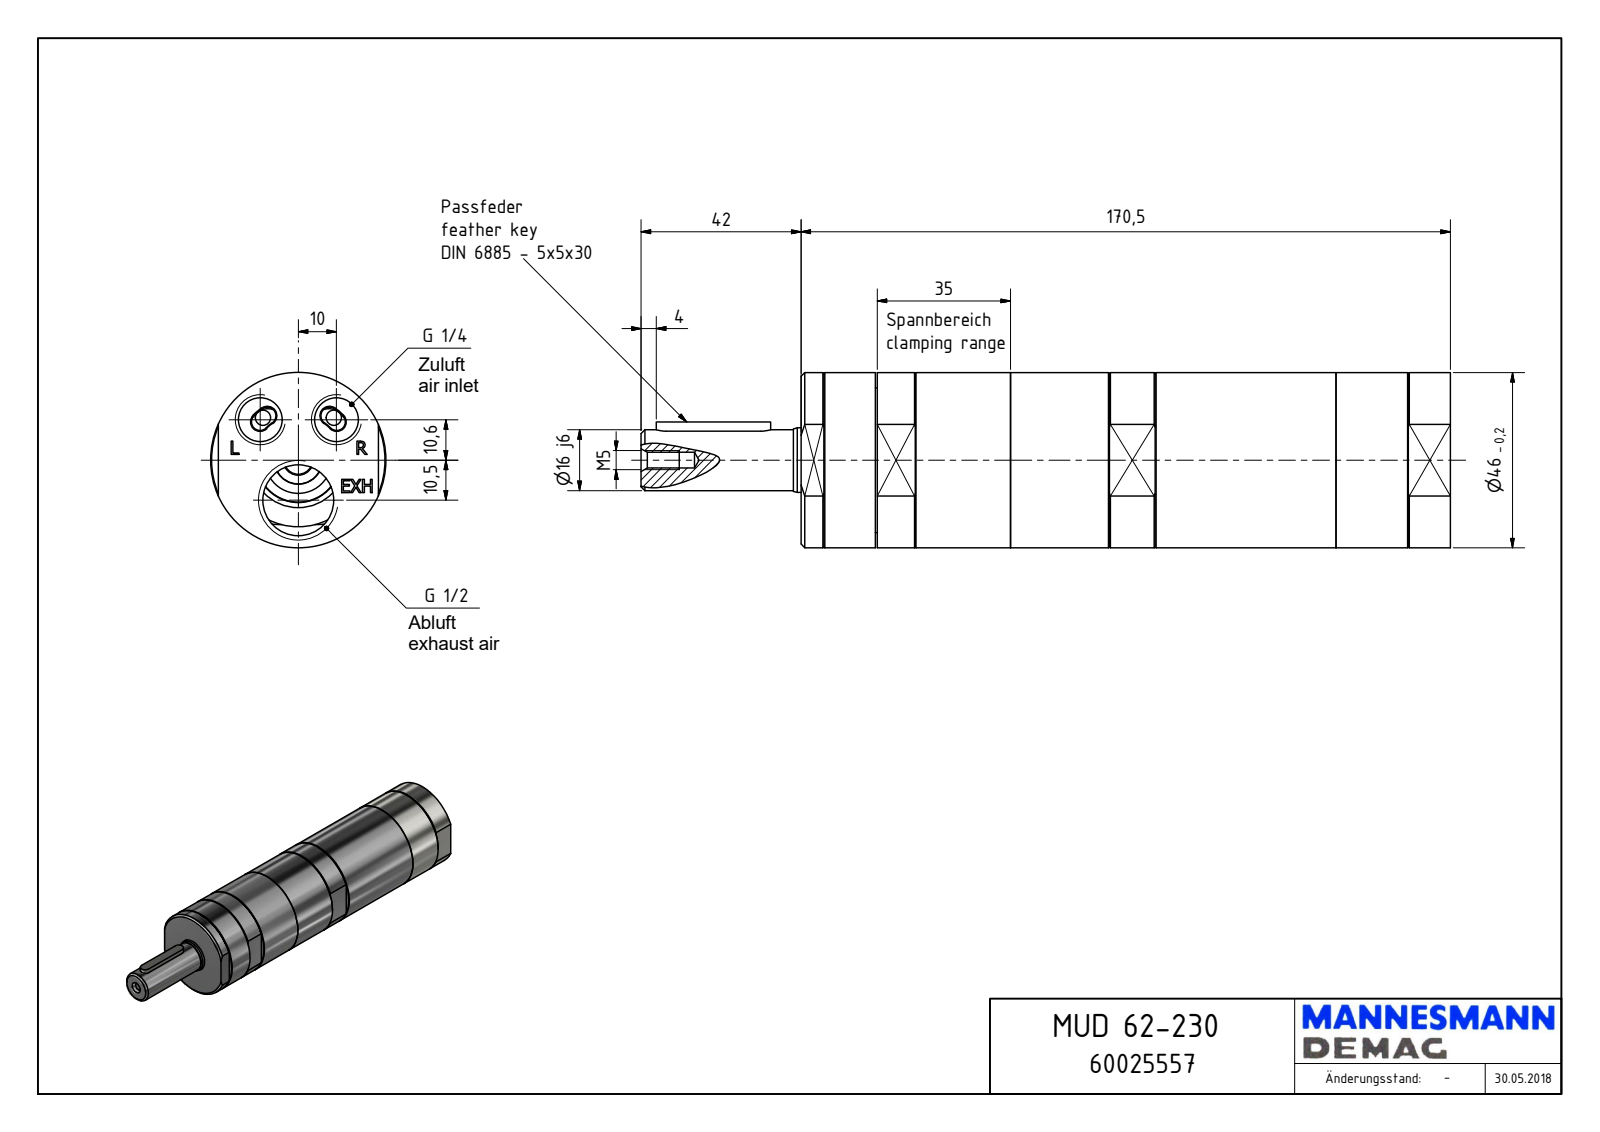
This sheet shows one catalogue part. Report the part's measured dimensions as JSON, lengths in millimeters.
{"part_name": "MUD 62-230_60025557", "step_written_by": "Autodesk Inventor 2018 (AUTOMOTIVE_DESIGN)", "units": "millimeters", "bodies": {"solids": 1, "faces": 165, "planar": 98, "cylindrical": 32, "other": 35}, "overall_size": [212.5, 46, 46], "volume_mm3": 284584, "surface_area_mm2": 34508, "round_holes": [[11.45, 2], [4.13, 1], [17.5, 1], [18.63, 1], [23, 1], [38, 1], [38.38, 1]], "round_bosses_or_shafts": [[46, 1], [33.85, 1], [16.95, 1], [16, 1]], "partial_cylinders_radius": [[2.5, 2], [5, 2]], "face_to_face_distances": [170.5, 42, 8, 162.5, 20, 142.5, 150.5, 19.5, 0.5, 143], "hole_center_spacings": [14.57, 23.35, 10.5, 20]}
